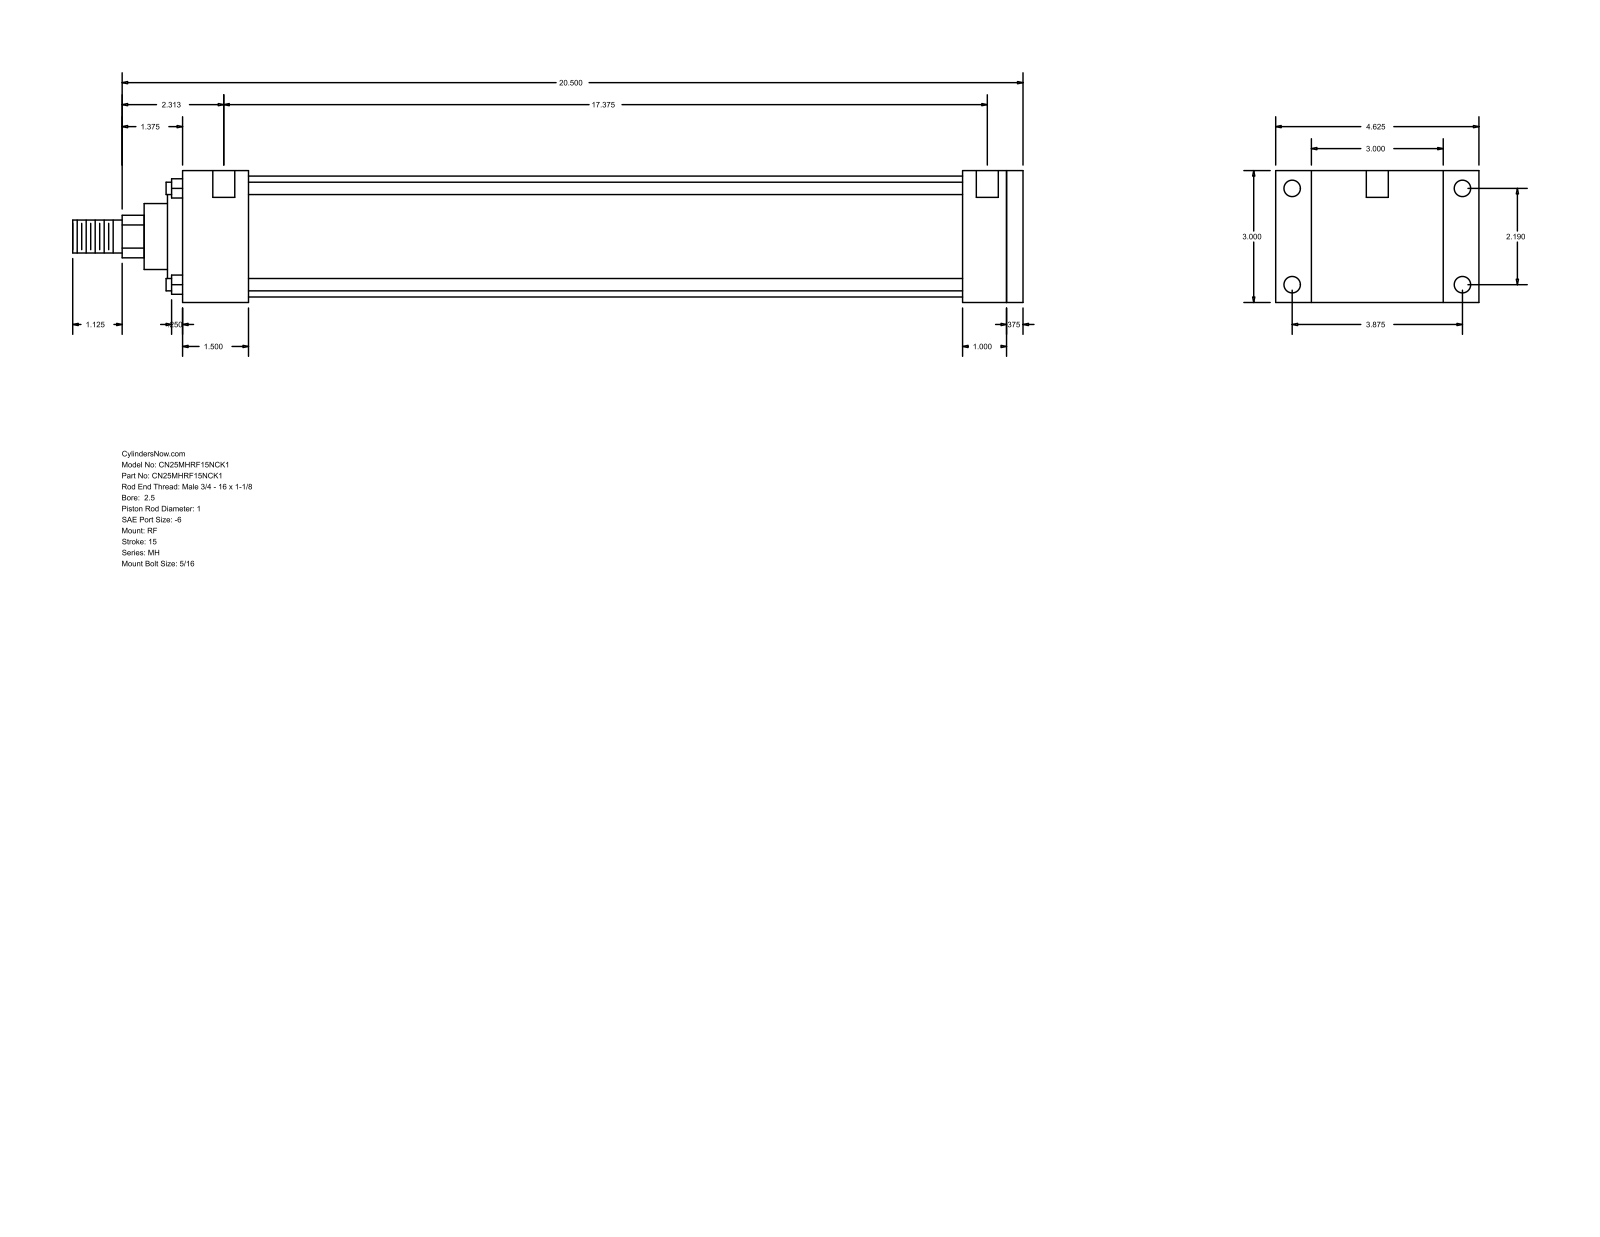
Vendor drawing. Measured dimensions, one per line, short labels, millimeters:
name: MH_RF__0250_1
written by: GSSL Pune (CONFIG_CONTROL_DESIGN)
unit: mm
bodies: 0 solids, 94 faces (65 planar, 29 cylindrical, 0 other)
size: 549.27 × 117.47 × 76.2
holes: 4× ⌀5.56, 4× ⌀9.53, 2× ⌀12.7
bosses: 4× ⌀7.14, 1× ⌀69.85, 1× ⌀60.33, 1× ⌀38.1, 1× ⌀25.4, 1× ⌀19.05
rounds: 1× R12.29
face distances: 76.2, 9.52, 485.78, 476.26, 450.85, 25.41, 34.93, 38.11, 412.74, 438.15
hole spacings: 55.62, 98.42, 113.05, 449.26, 3.18, 4.76, 441.32, 444.5
